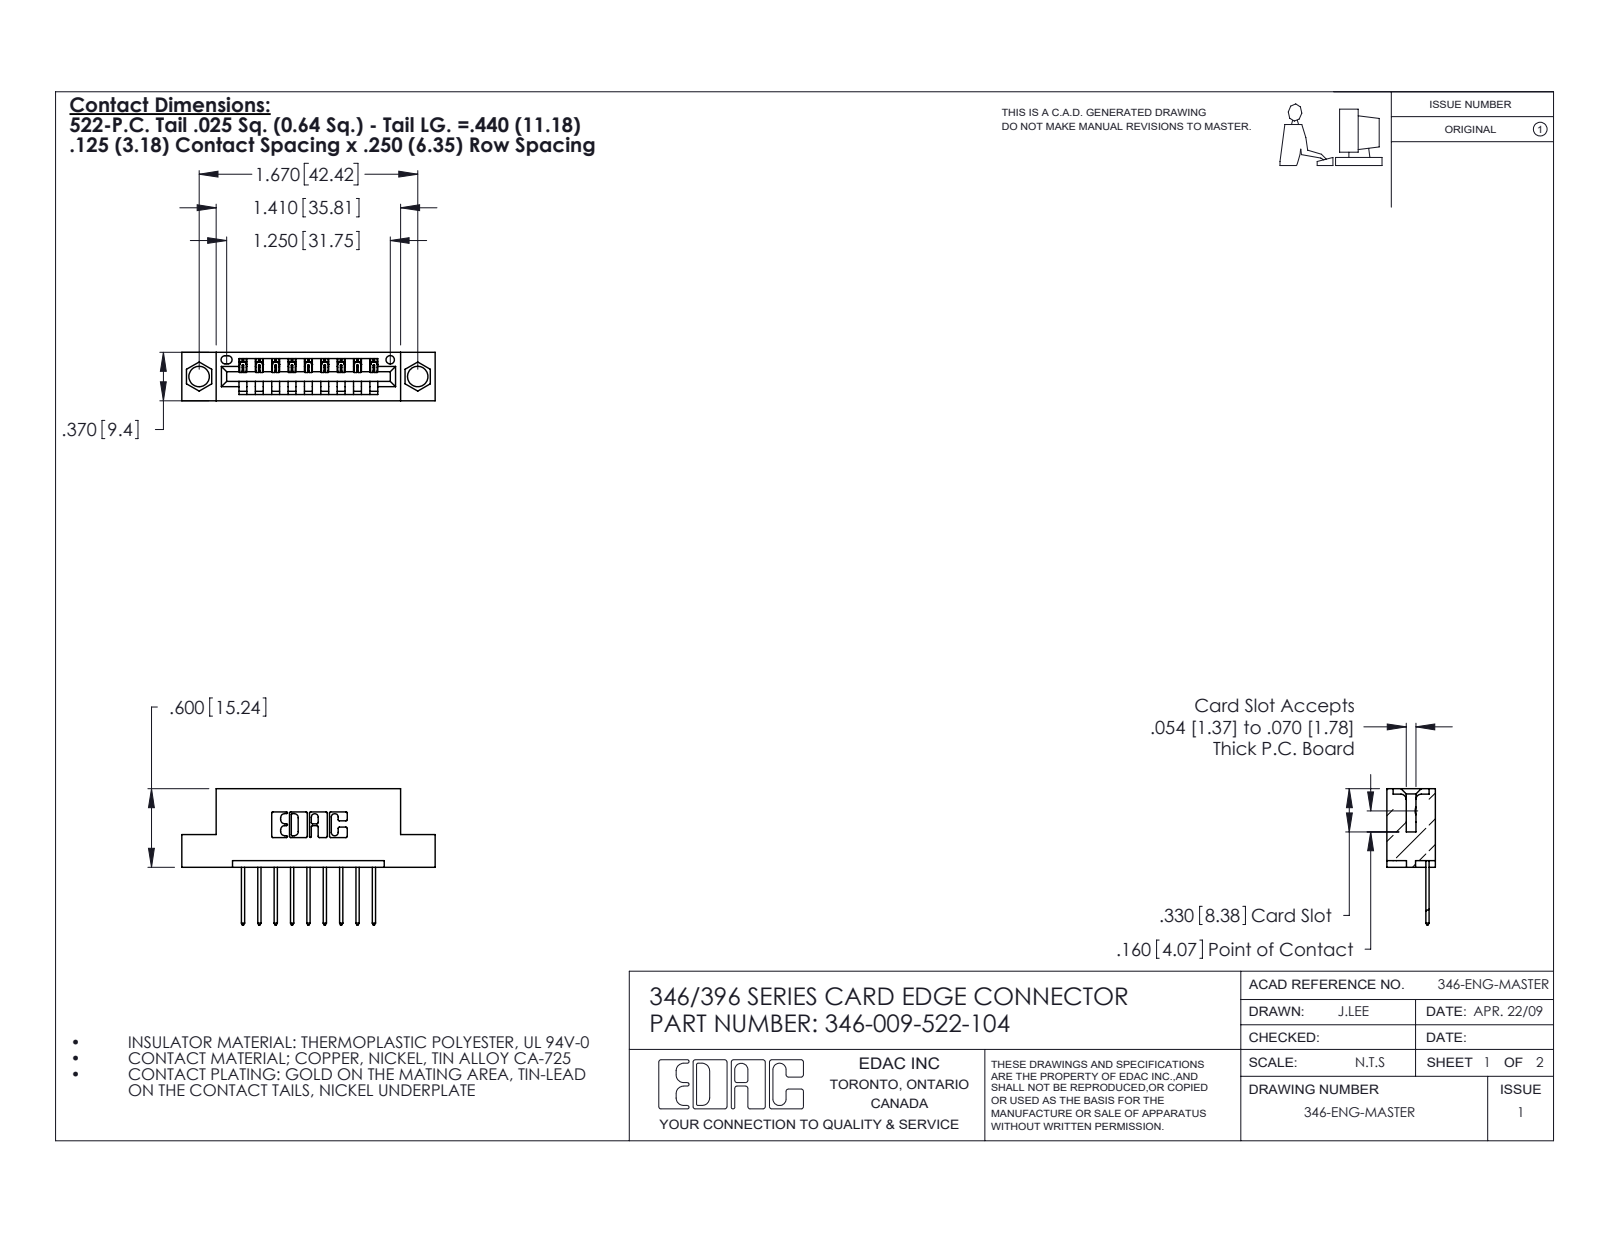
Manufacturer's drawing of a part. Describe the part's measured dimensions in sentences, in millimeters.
The part is named "345-292-001_345-293-122; 346 Part_Flush Mounting Lugs - 0.156 Dia-TH; 346-009-522-104". Its 3-D file was written by "SolidWorks 2020 (CONFIG_CONTROL_DESIGN)". It is 10 solids with 658 faces: 450 planar, 208 cylindrical and 0 other. Overall it measures 49.1 by 26.4 by 9.4 millimeters. Its volume is 4 380 cubic millimeters and its surface area 4 979 square millimeters. Round holes: 2 of diameter 4, 1 of diameter 1.6. Partial cylindrical surfaces (rounded edges, fillets, slot ends): 22 of radius 0.3, 18 of radius 0.2, 18 of radius 0.3, 6 of radius 0.2, 6 of radius 0.8, 3 of radius 0.7, 2 of radius 0.8, 2 of radius 1. The main face-to-face distances are 6.4, 1.2, 8.2, 9.4, 1.8, 7.6, 0.6, 3.8, 5.6, 2.5. The hole center spacings are 6.2, 37.2, 42.4.
